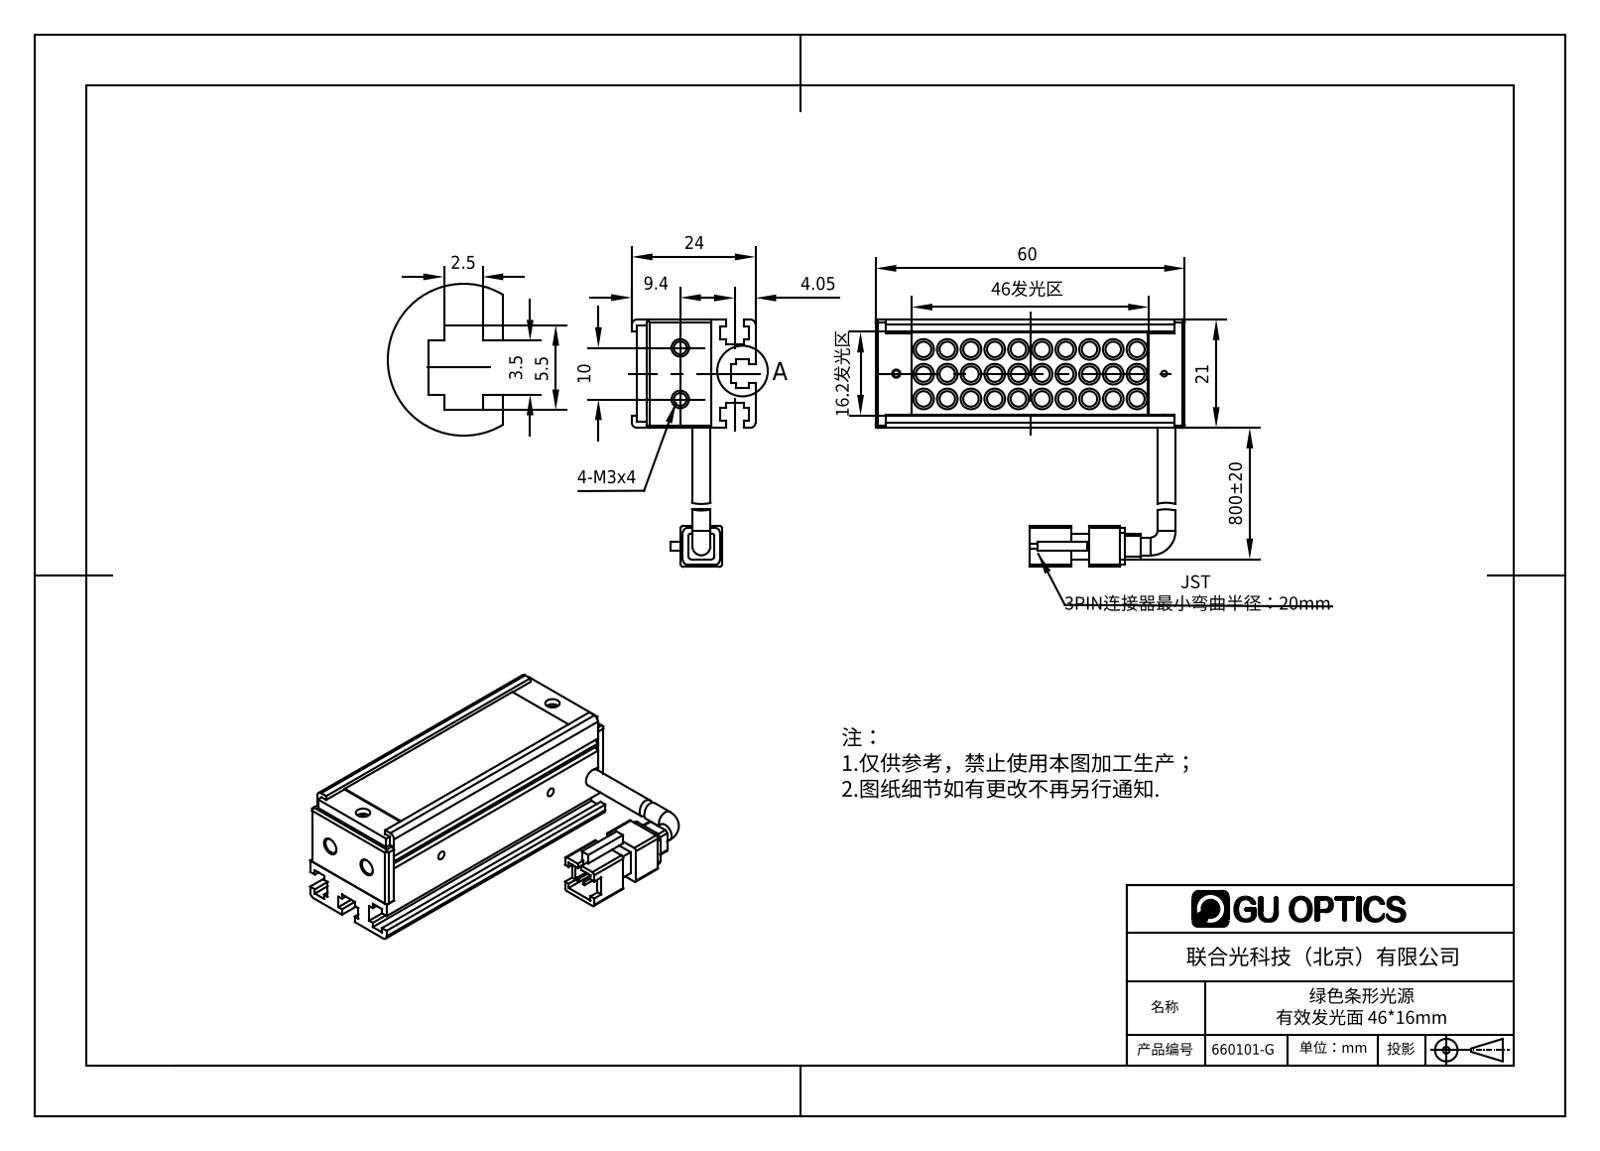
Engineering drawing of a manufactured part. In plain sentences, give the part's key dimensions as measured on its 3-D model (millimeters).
The part is named "660101-B". Its 3-D file was written by "SolidWorks 2016 (AUTOMOTIVE_DESIGN)". It is 7 solids with 611 faces: 273 planar, 209 cylindrical and 129 other. Overall it measures 60 by 48 by 24 millimeters. Its volume is 21 804 cubic millimeters and its surface area 20 628 square millimeters. Round holes: 5 of diameter 1.6, 2 of diameter 1.5, 2 of diameter 1.7, 2 of diameter 2.5, 2 of diameter 2.8, 2 of diameter 3, 1 of diameter 1.1, 1 of diameter 1.25, 1 of diameter 2. Round bosses or shafts: 30 of diameter 4, 30 of diameter 3, 2 of diameter 3.5. Partial cylindrical surfaces (rounded edges, fillets, slot ends): 12 of radius 1, 8 of radius 0.5, 4 of radius 0.6, 1 of radius 1.65. The main face-to-face distances are 2.4, 1, 4, 18.6, 8.6, 12.6, 21, 16.2, 2, 2.2. The hole center spacings are 52, 7, 11.12, 12.25, 41.03, 41.35, 52.47, 10.
